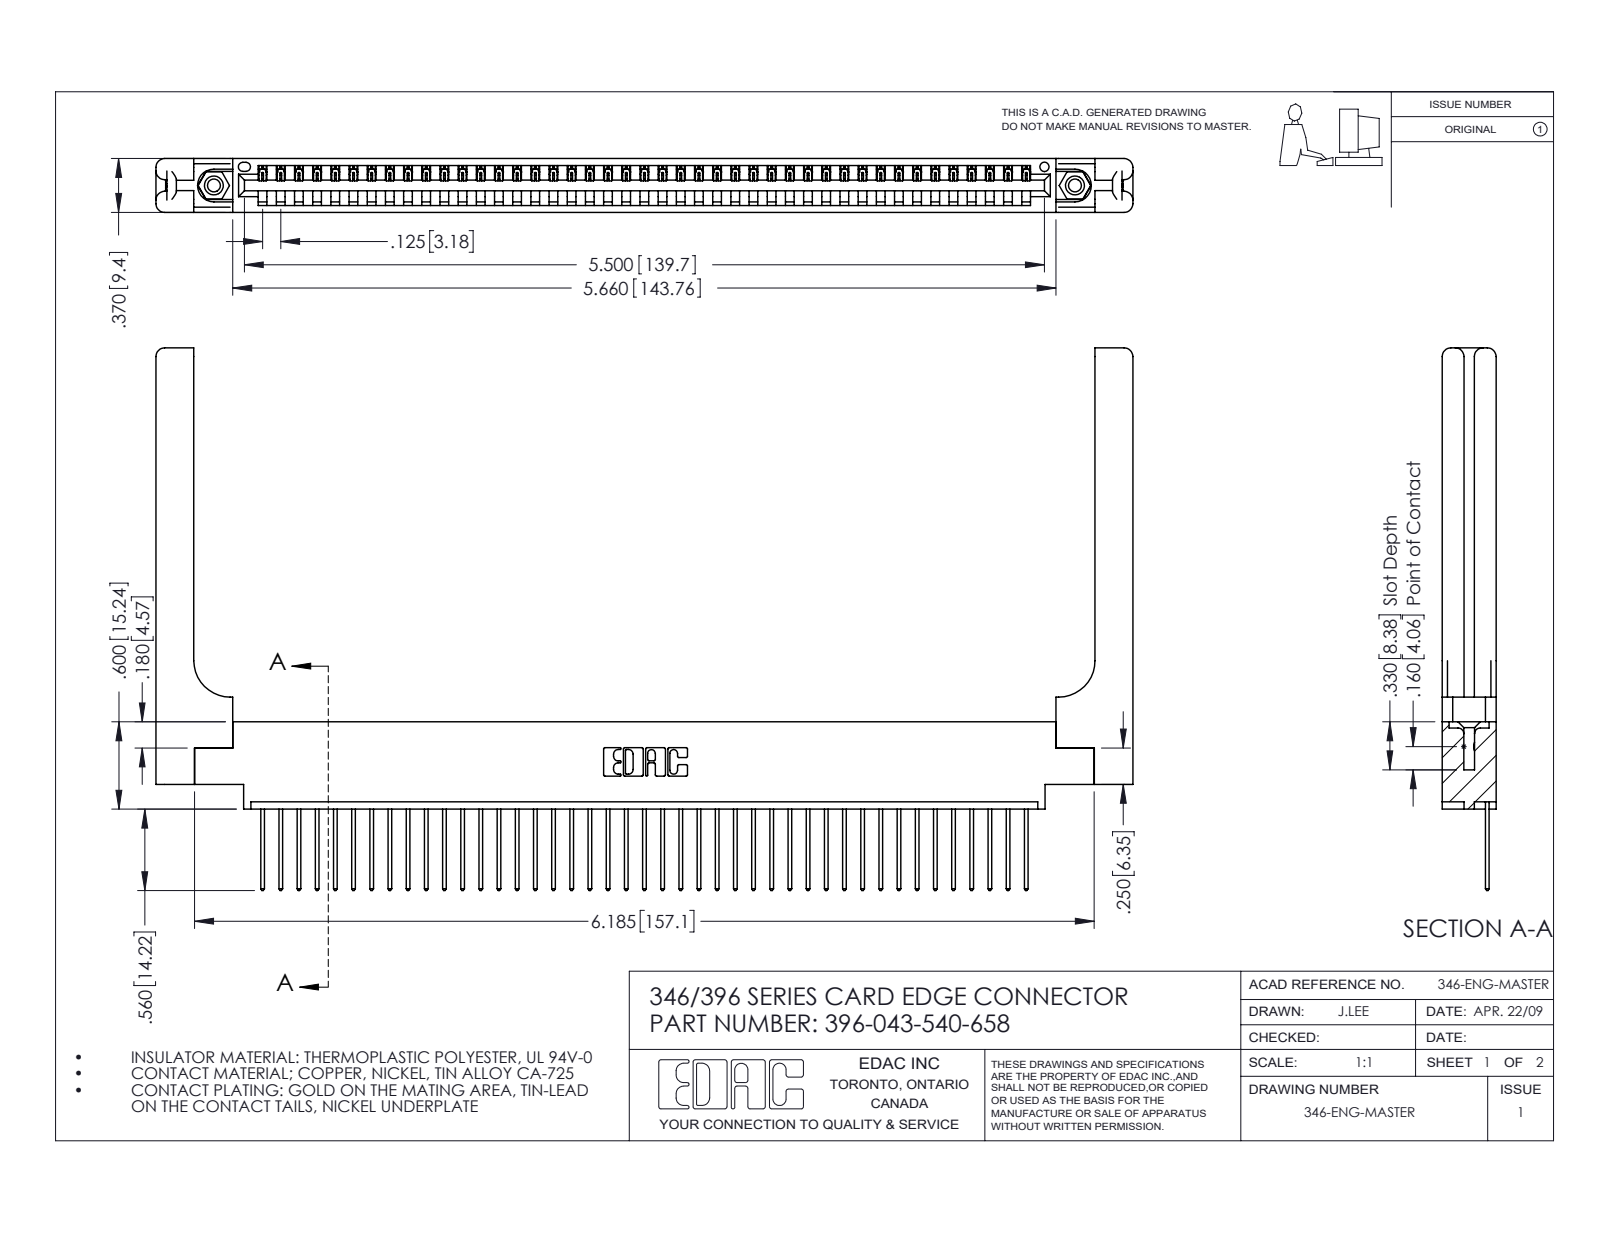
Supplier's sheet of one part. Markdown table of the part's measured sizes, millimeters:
| quantity | value |
| --- | --- |
| part name | 346 Part_0.170 Offset - 0.156 Dia-TH; 396-043-540-658; 345-250-001_345-250-001-102; 345-292-001_345-293-140 (+1 more) |
| STEP written by | SolidWorks 2016 (CONFIG_CONTROL_DESIGN) |
| units | millimeters |
| bodies | 48 solids, 2876 faces (1948 planar, 868 cylindrical, 60 other) |
| overall size | 170.6 × 94.7 × 9.4 |
| volume | 23 760 mm³ |
| surface area | 26 060 mm² |
| round holes (diameter × count) | 2.3 × 2, 3.2 × 2, 4 × 2, 1.6 × 1 |
| round bosses / shafts (diameter × count) | 3.9 × 2 |
| partial cylindrical surfaces (radius × count) | 0.2 × 86, 0.3 × 86, 0.3 × 22, 1.5 × 16, 0.2 × 6, 0.8 × 6, 0.7 × 3, 0.8 × 2 |
| main face-to-face distances | 9.4, 1.2, 8.2, 1.8, 3.8, 3.8, 6.4, 7.6, 0.6, 5.6 |
| hole center spacings | 6.2, 145.1, 150.4 |
